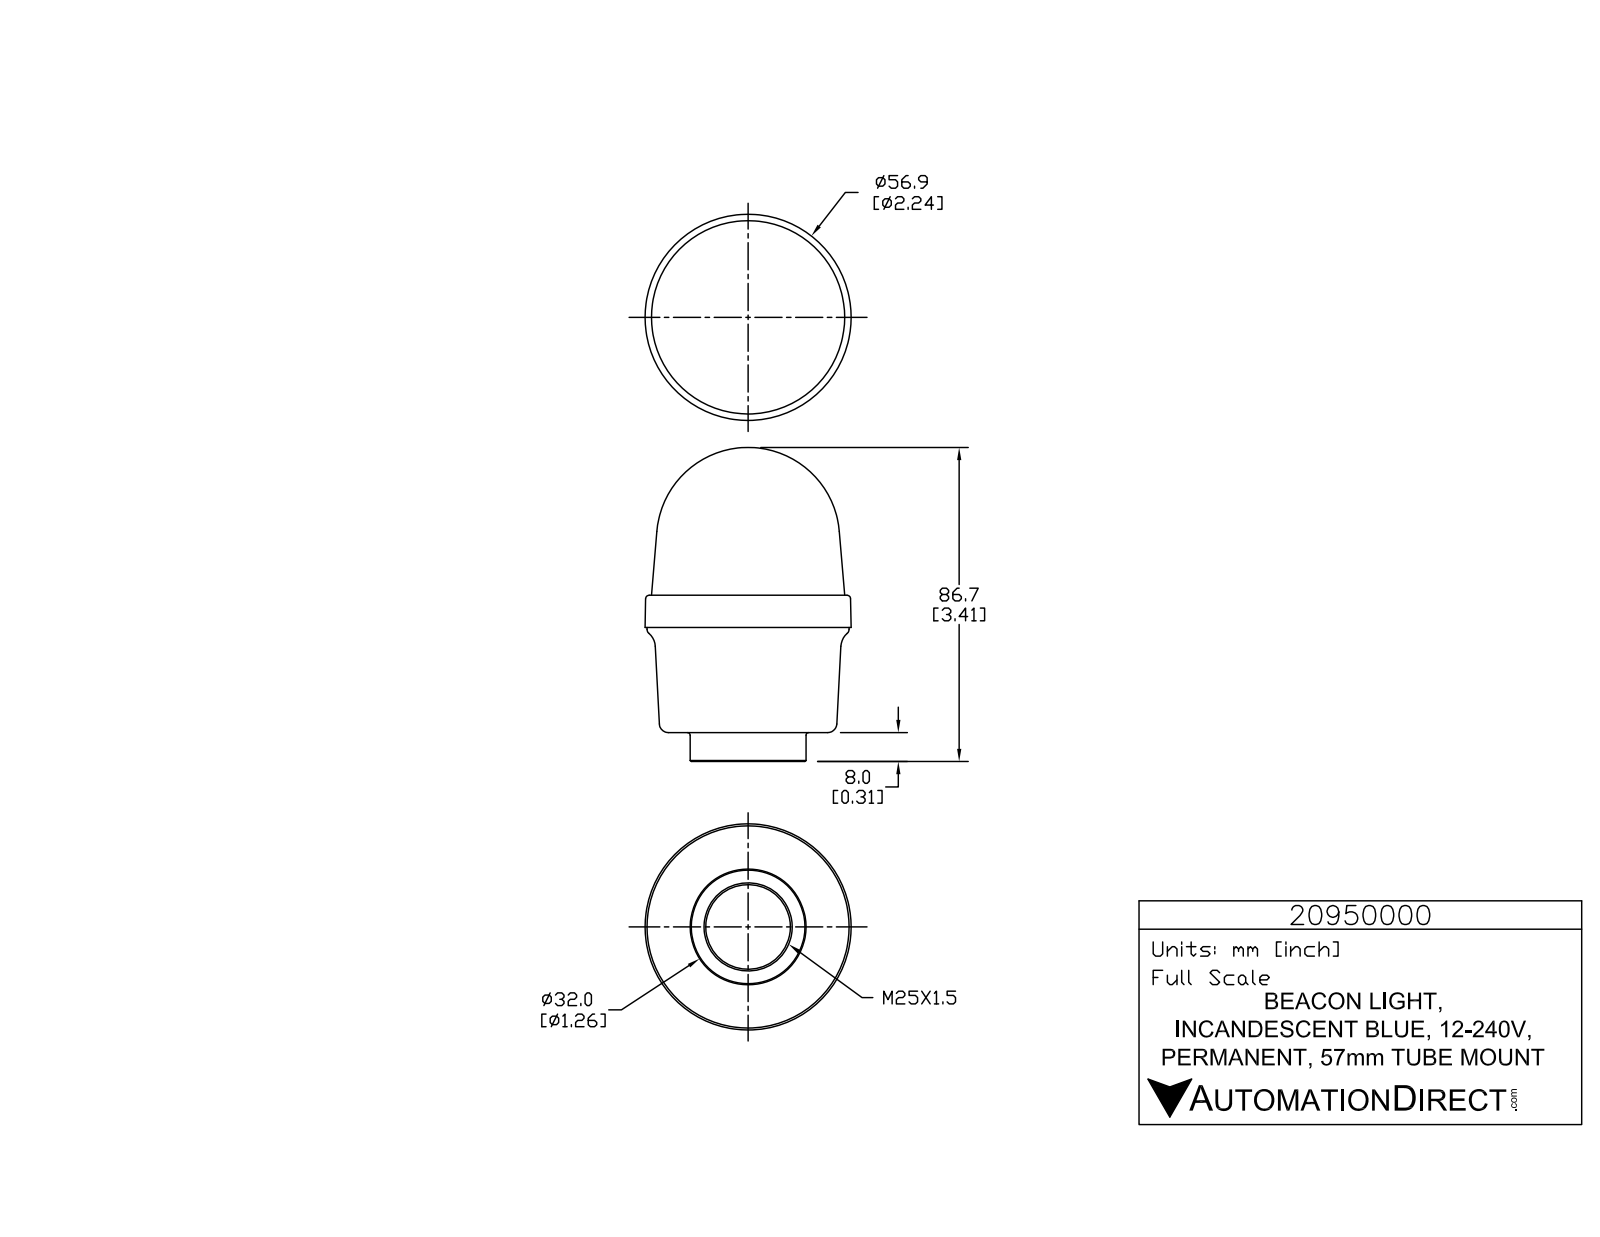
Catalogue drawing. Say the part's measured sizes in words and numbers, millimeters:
The part is named "20950000". Its 3-D file was written by "SolidWorks 2015 (AUTOMOTIVE_DESIGN)". It is 1 solid with 787 faces: 524 planar, 168 cylindrical and 95 other. Overall it measures 86.7 by 56.9 by 56.9 millimeters. Its volume is 150 600 cubic millimeters and its surface area 16 310 square millimeters. Round holes: 3 of diameter 1, 1 of diameter 23.4. Round bosses or shafts: 3 of diameter 5.7, 3 of diameter 1.4, 1 of diameter 55.8, 1 of diameter 32. Partial cylindrical surfaces (rounded edges, fillets, slot ends): 6 of radius 0.2, 6 of radius 0.2, 6 of radius 0.2, 6 of radius 3.3, 3 of radius 0.1, 3 of radius 0.1, 3 of radius 0.2, 3 of radius 0.2. The main face-to-face distances are 8, 37.9, 45.9, 8.9, 29, 37, 17.7, 8.8, 46.7, 54.7.
